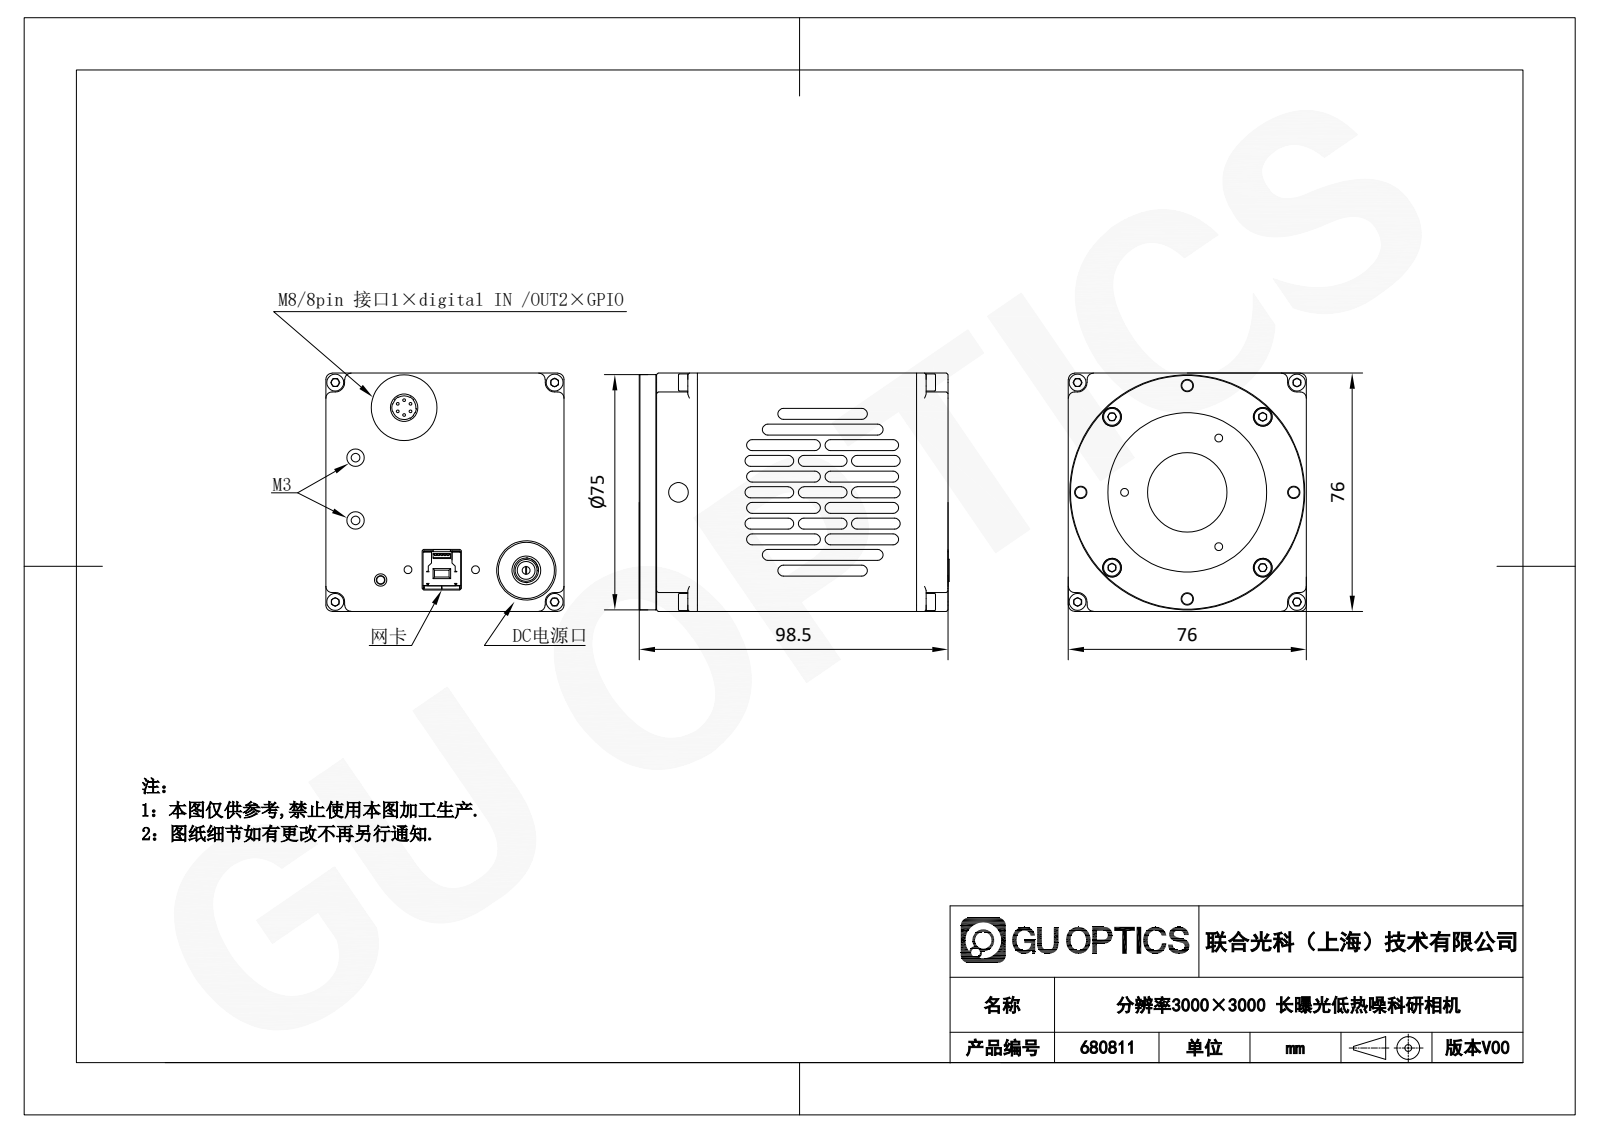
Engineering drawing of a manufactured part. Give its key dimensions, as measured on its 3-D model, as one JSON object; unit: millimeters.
{"part_name": "SONY_IMX533_6_1.stp; CROSS_RECESSED_PAN_HEAD_S-38587.stp; HOUSSING2_3_4_5_1_1_1.stp; SCHIELDING2_3_4_5_1_1_1.stp (+8 more)", "step_written_by": "SolidWorks 2024 (CONFIG_CONTROL_DESIGN)", "units": "millimeters", "bodies": {"solids": 43, "faces": 2930, "planar": 1642, "cylindrical": 1042, "other": 246}, "overall_size": [98.84, 76, 76], "volume_mm3": 169400, "surface_area_mm2": 105510, "round_holes": [[2.5, 14], [3.4, 8], [4, 6], [3.5, 4], [6, 4], [2.9, 3], [0.8, 2], [5.7, 2], [6.35, 2], [0.37, 1], [6.6, 1], [7.4, 1]], "round_bosses_or_shafts": [[0.8, 174], [5.5, 8], [3, 8], [0.7, 6], [11, 2], [2.5, 2], [1.2, 2], [75, 1]], "partial_cylinders_radius": [[1.75, 42], [0.3, 37], [0.5, 34], [1, 27], [5, 16], [2, 14], [0.31, 11], [0.4, 8]], "face_to_face_distances": [76, 3, 2, 10, 74, 70, 5.5, 5, 13, 1.5], "hole_center_spacings": [26.02, 34, 35.01, 48.08, 60.05, 62.82, 77.37, 15.5]}
